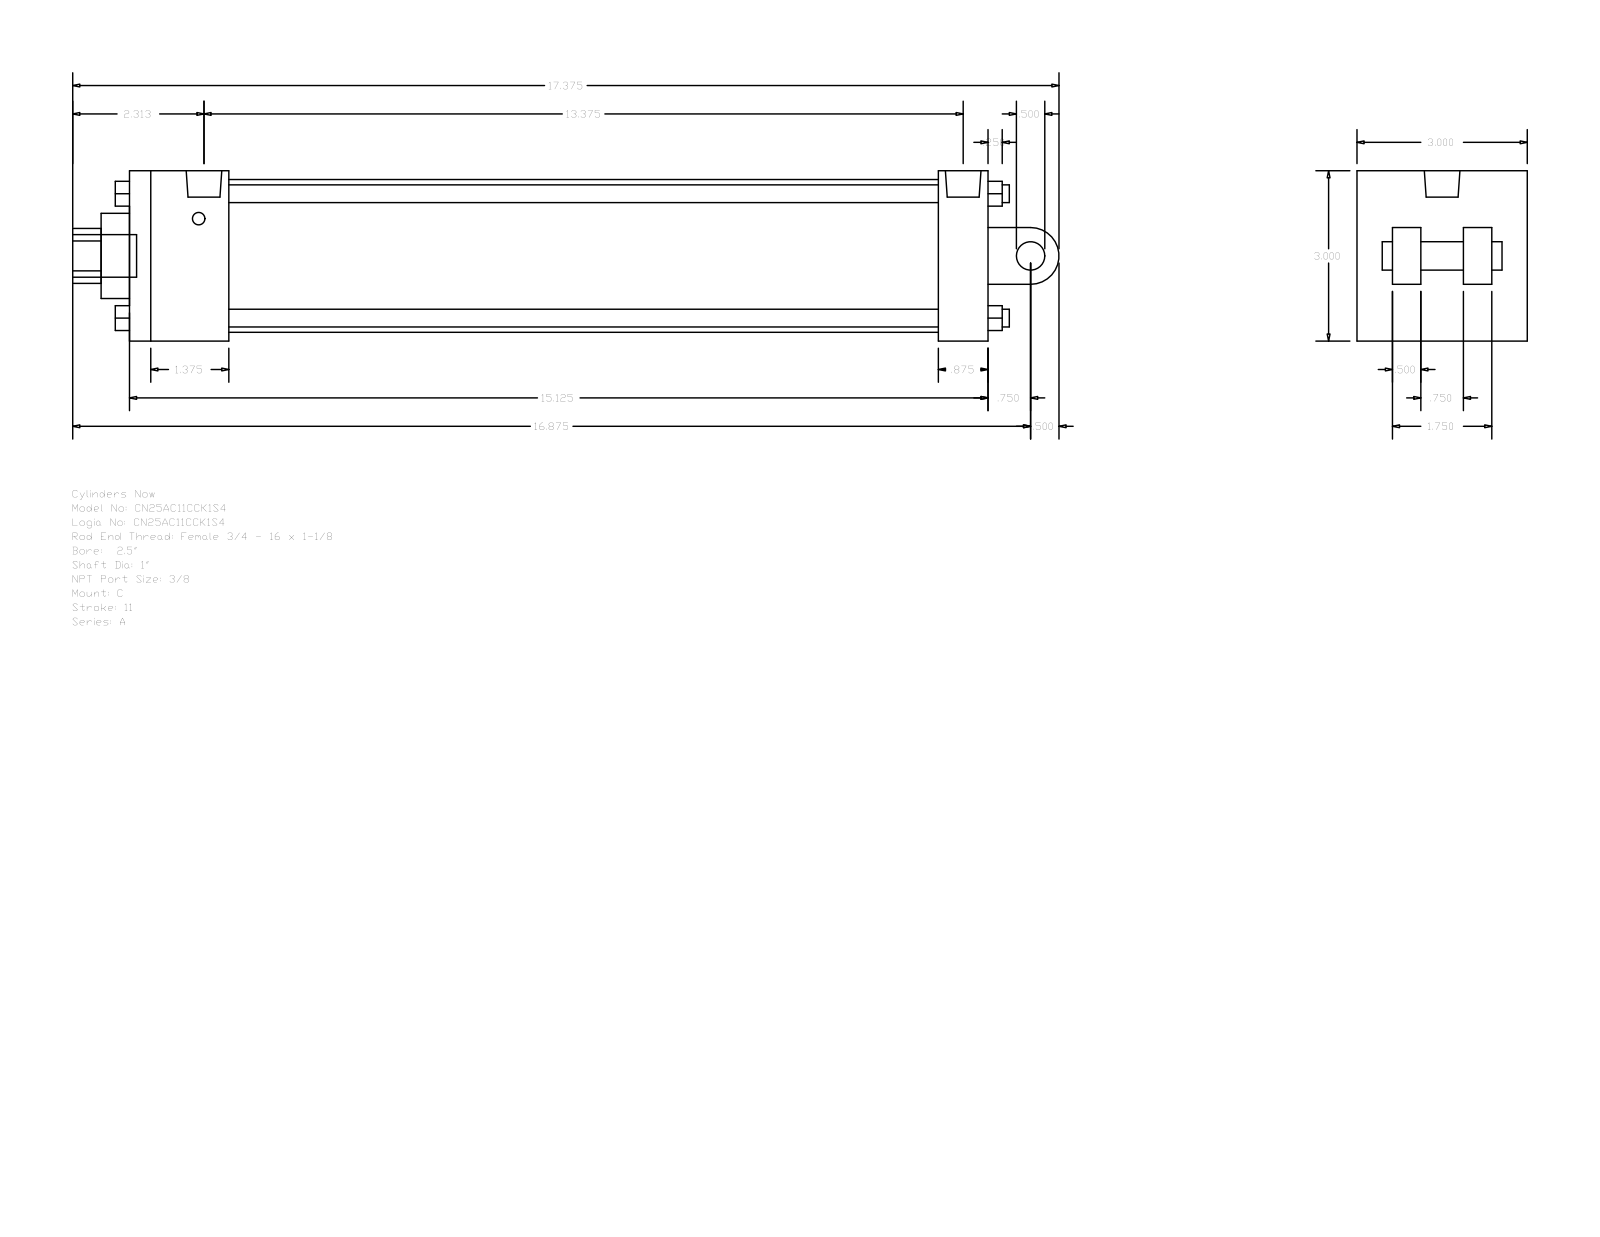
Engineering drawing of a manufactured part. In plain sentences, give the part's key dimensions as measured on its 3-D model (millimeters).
The part is named "A_C__0250_1". Its 3-D file was written by "GSSL Pune (CONFIG_CONTROL_DESIGN)". It is 0 solids with 135 faces: 102 planar, 33 cylindrical and 0 other. Overall it measures 441.32 by 76.2 by 76.2 millimeters. Round holes: 2 of diameter 5.56, 1 of diameter 15.93, 1 of diameter 25.4, 1 of diameter 38.1, 1 of diameter 68.33. Round bosses or shafts: 4 of diameter 7.94, 2 of diameter 5.56, 1 of diameter 19.05, 1 of diameter 15.93, 1 of diameter 12.7. Partial cylindrical surfaces (rounded edges, fillets, slot ends): 1 of radius 12.29, 1 of radius 12.7. The main face-to-face distances are 76.2, 384.17, 12.7, 44.45, 361.95, 317.5, 339.72, 22.22, 15.87, 25.4. The hole center spacings are 2.38.
